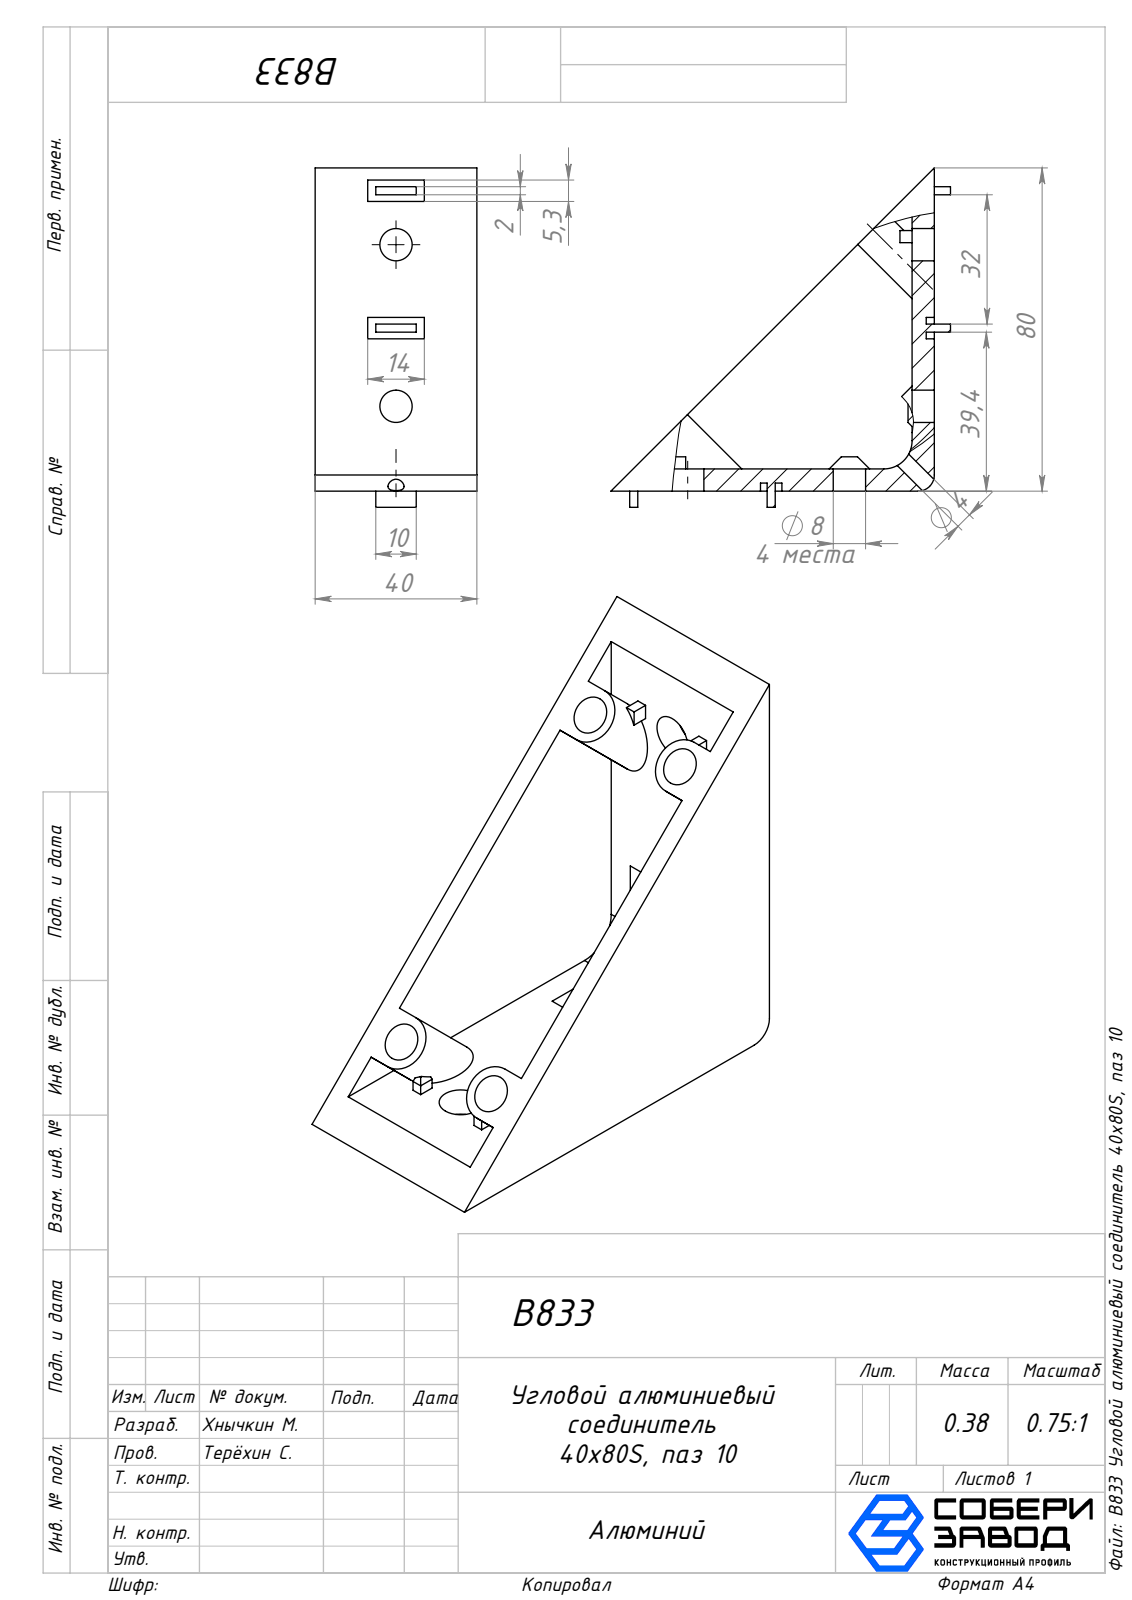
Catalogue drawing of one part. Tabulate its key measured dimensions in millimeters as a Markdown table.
| quantity | value |
| --- | --- |
| part name | B833 Угловой алюминиевый соединитель 40х80S, паз 10 |
| STEP written by | SolidWorks 2025 (AUTOMOTIVE_DESIGN) |
| units | millimeters |
| bodies | 1 solid, 131 faces (107 planar, 24 cylindrical, 0 other) |
| overall size | 84 × 84 × 40 |
| volume | 53 695 mm³ |
| surface area | 26 427 mm² |
| round holes (diameter × count) | 7 × 4, 8 × 4, 4 × 1 |
| partial cylindrical surfaces (radius × count) | 5.25 × 4, 4 × 1, 7 × 1 |
| main face-to-face distances | 36, 4, 5.5, 40, 32, 2, 34, 73.35, 39.35, 1.65 |
| hole center spacings | 36.96, 23.5, 40, 70.09, 73.92 |
